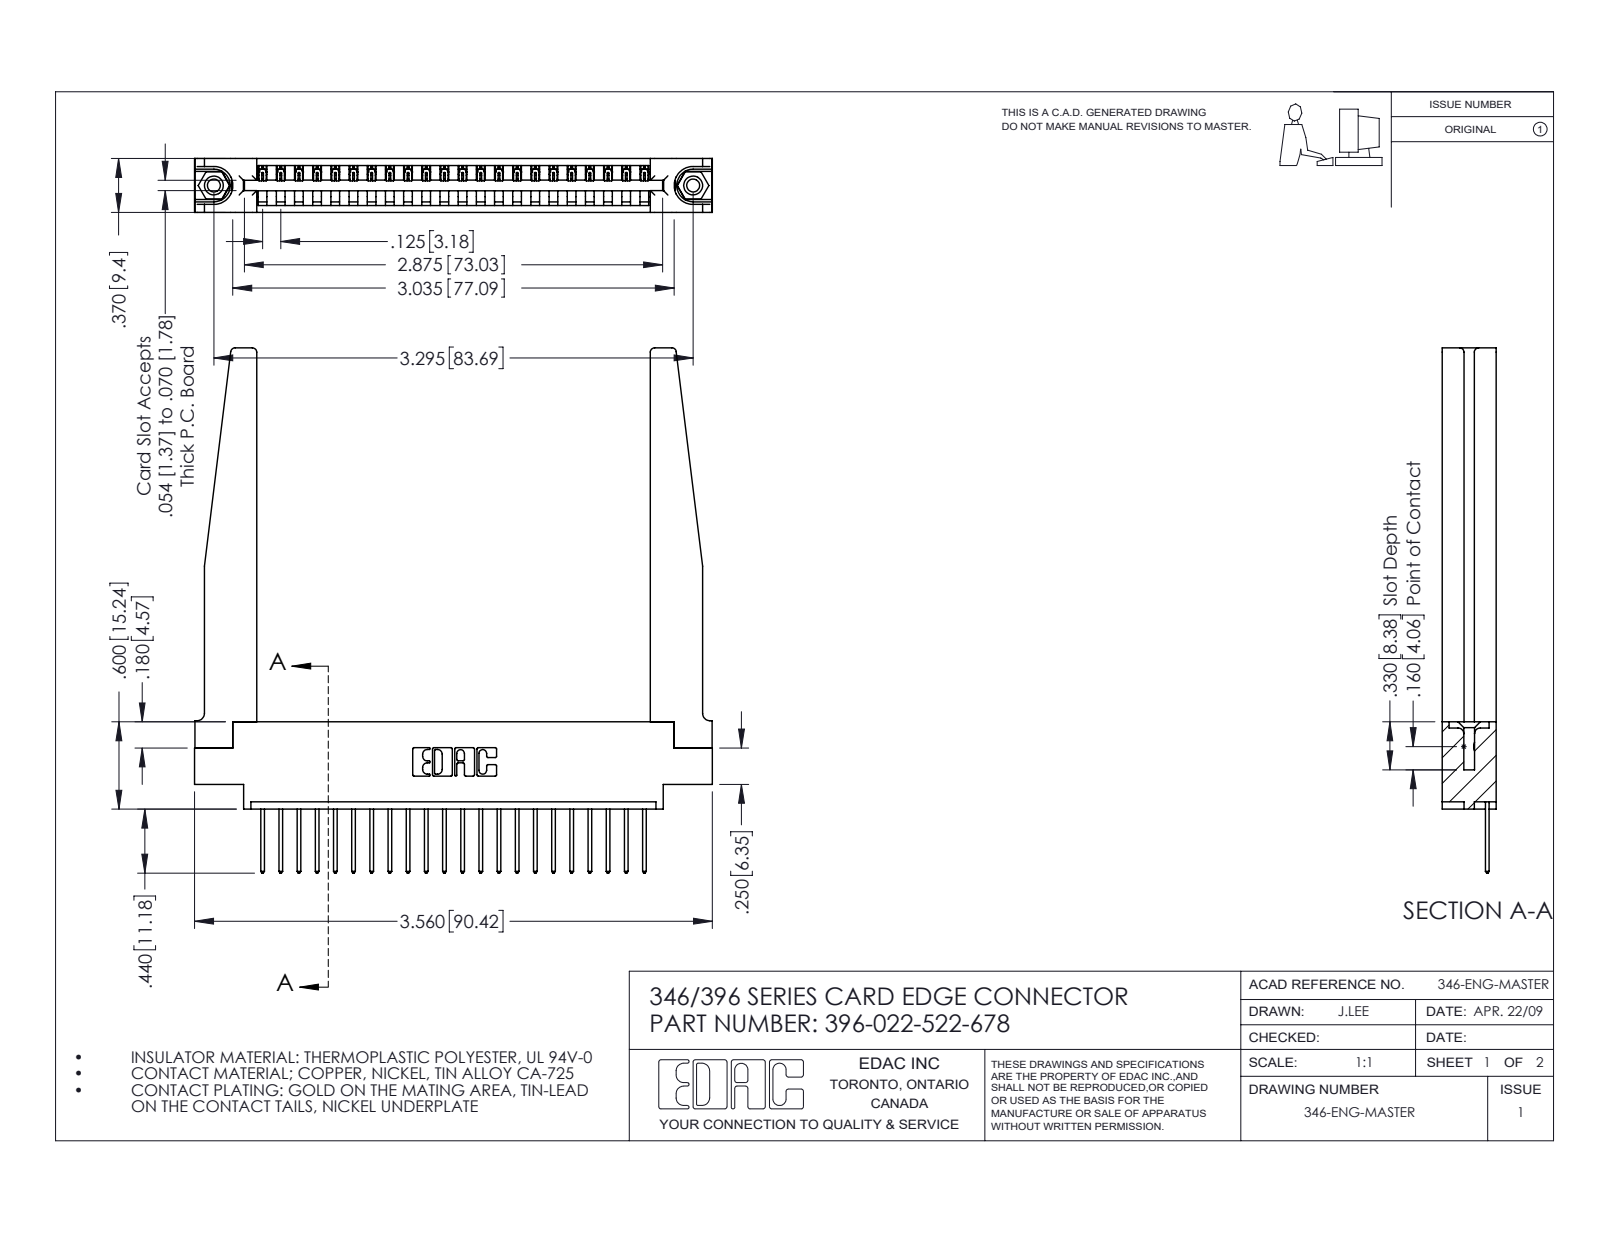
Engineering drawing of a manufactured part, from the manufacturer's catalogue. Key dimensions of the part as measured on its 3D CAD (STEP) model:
Part name (STEP PRODUCT): 346-220-078_345-220-078; 345-292-001_345-293-122; 396-022-522-678; 346 Part_0.170 Offset - 0.156 Dia-TH (+1 more)
STEP written by: SolidWorks 2016 (CONFIG_CONTROL_DESIGN)
Units: inches
Bodies: 27 solids, 1636 faces (1102 planar, 482 cylindrical, 52 other)
Overall size (bounding box): 3.61 × 3.56 × 0.37
Volume: 0.932 in³ · Surface area: 26.38 in²
Round holes (diameter × count): ⌀0.089 ×2, ⌀0.125 ×2, ⌀0.156 ×2, ⌀0.064 ×1
Round bosses / shafts (diameter × count): ⌀0.155 ×2
Partial cylindrical surfaces — rounded edges, fillets, slot ends (radius × count): R0.006 ×44, R0.01 ×44, R0.01 ×22, R0.03 ×8, R0.007 ×6, R0.031 ×6, R0.026 ×3, R0.031 ×2
Main face-to-face distances: 0.37, 0.072, 0.048, 0.322, 0.148, 0.15, 0.25, 0.298, 0.025, 0.222
Hole centre spacings: 0.246, 3.087, 3.295
